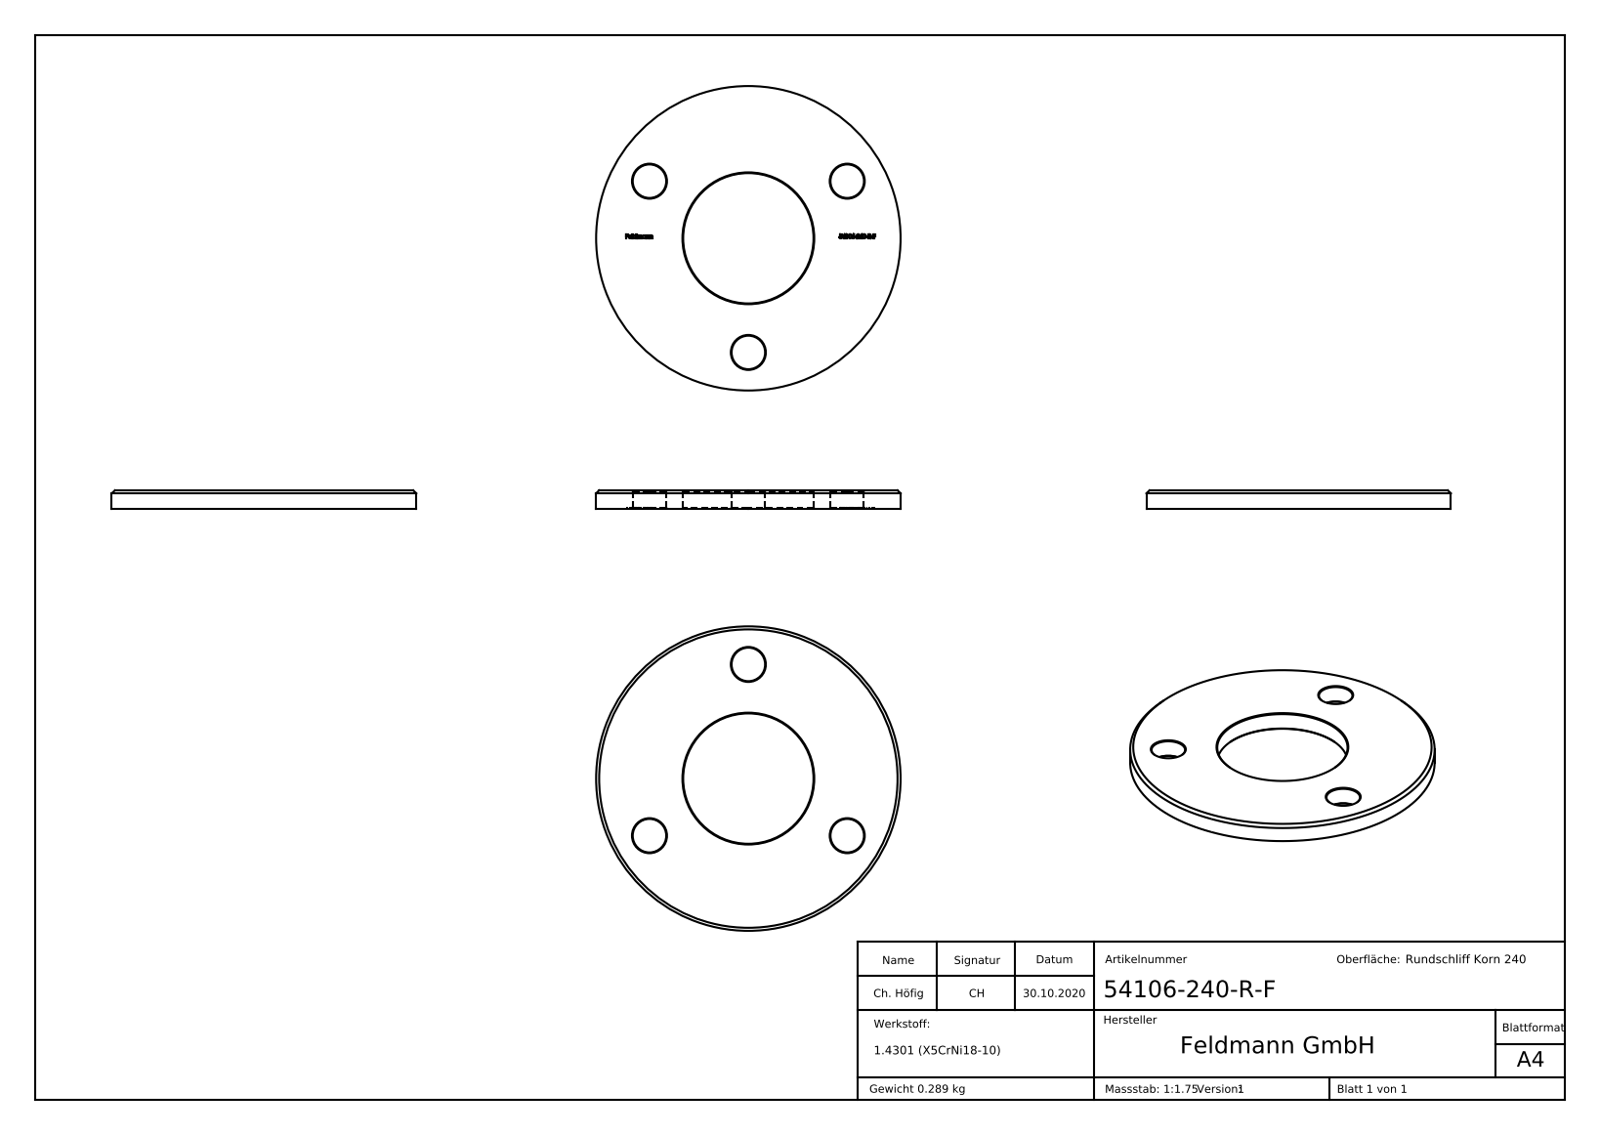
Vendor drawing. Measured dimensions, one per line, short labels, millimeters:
name: 54106-240-R-F
written by: SolidWorks 2018 (CONFIG_CONTROL_DESIGN)
unit: mm
bodies: 1 solid, 288 faces (166 planar, 10 cylindrical, 112 other)
size: 100 × 100 × 6
volume: 36 609 mm³; area: 15 331 mm²
holes: 3× ⌀11, 1× ⌀42.8
bosses: 1× ⌀100
face distances: 6, 5.9, 0.88, 2.02, 77.46, 0.44, 2.14, 77.34, 0.58, 70.42
hole spacings: 37.5, 64.95, 64.96
